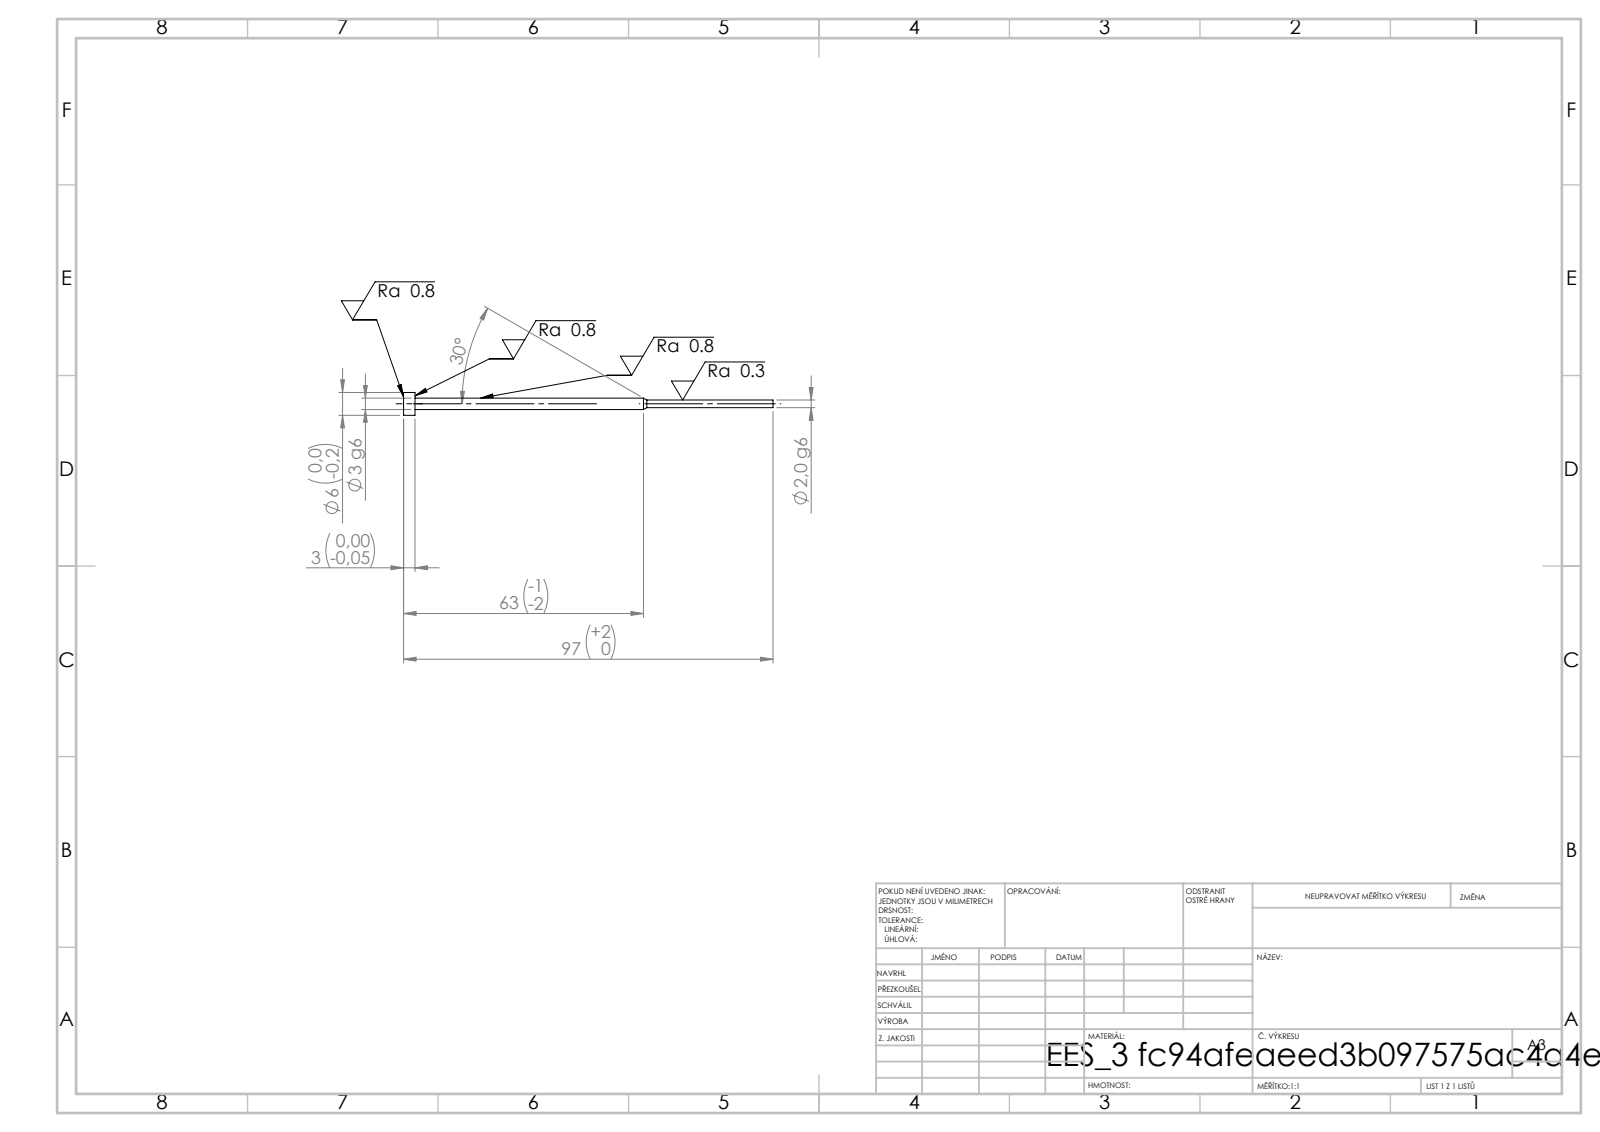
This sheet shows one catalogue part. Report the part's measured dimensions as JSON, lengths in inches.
{"step_written_by": "SolidWorks 2019 (CONFIG_CONTROL_DESIGN)", "units": "inches", "bodies": {"solids": 1, "faces": 11, "planar": 3, "cylindrical": 6, "other": 2}, "overall_size": [3.819, 0.236, 0.236], "volume_in3": 0.038, "surface_area_in2": 1.38, "round_bosses_or_shafts": [[0.236, 1], [0.118, 1], [0.079, 1]], "face_to_face_distances": [0.118, 3.701, 3.819]}
